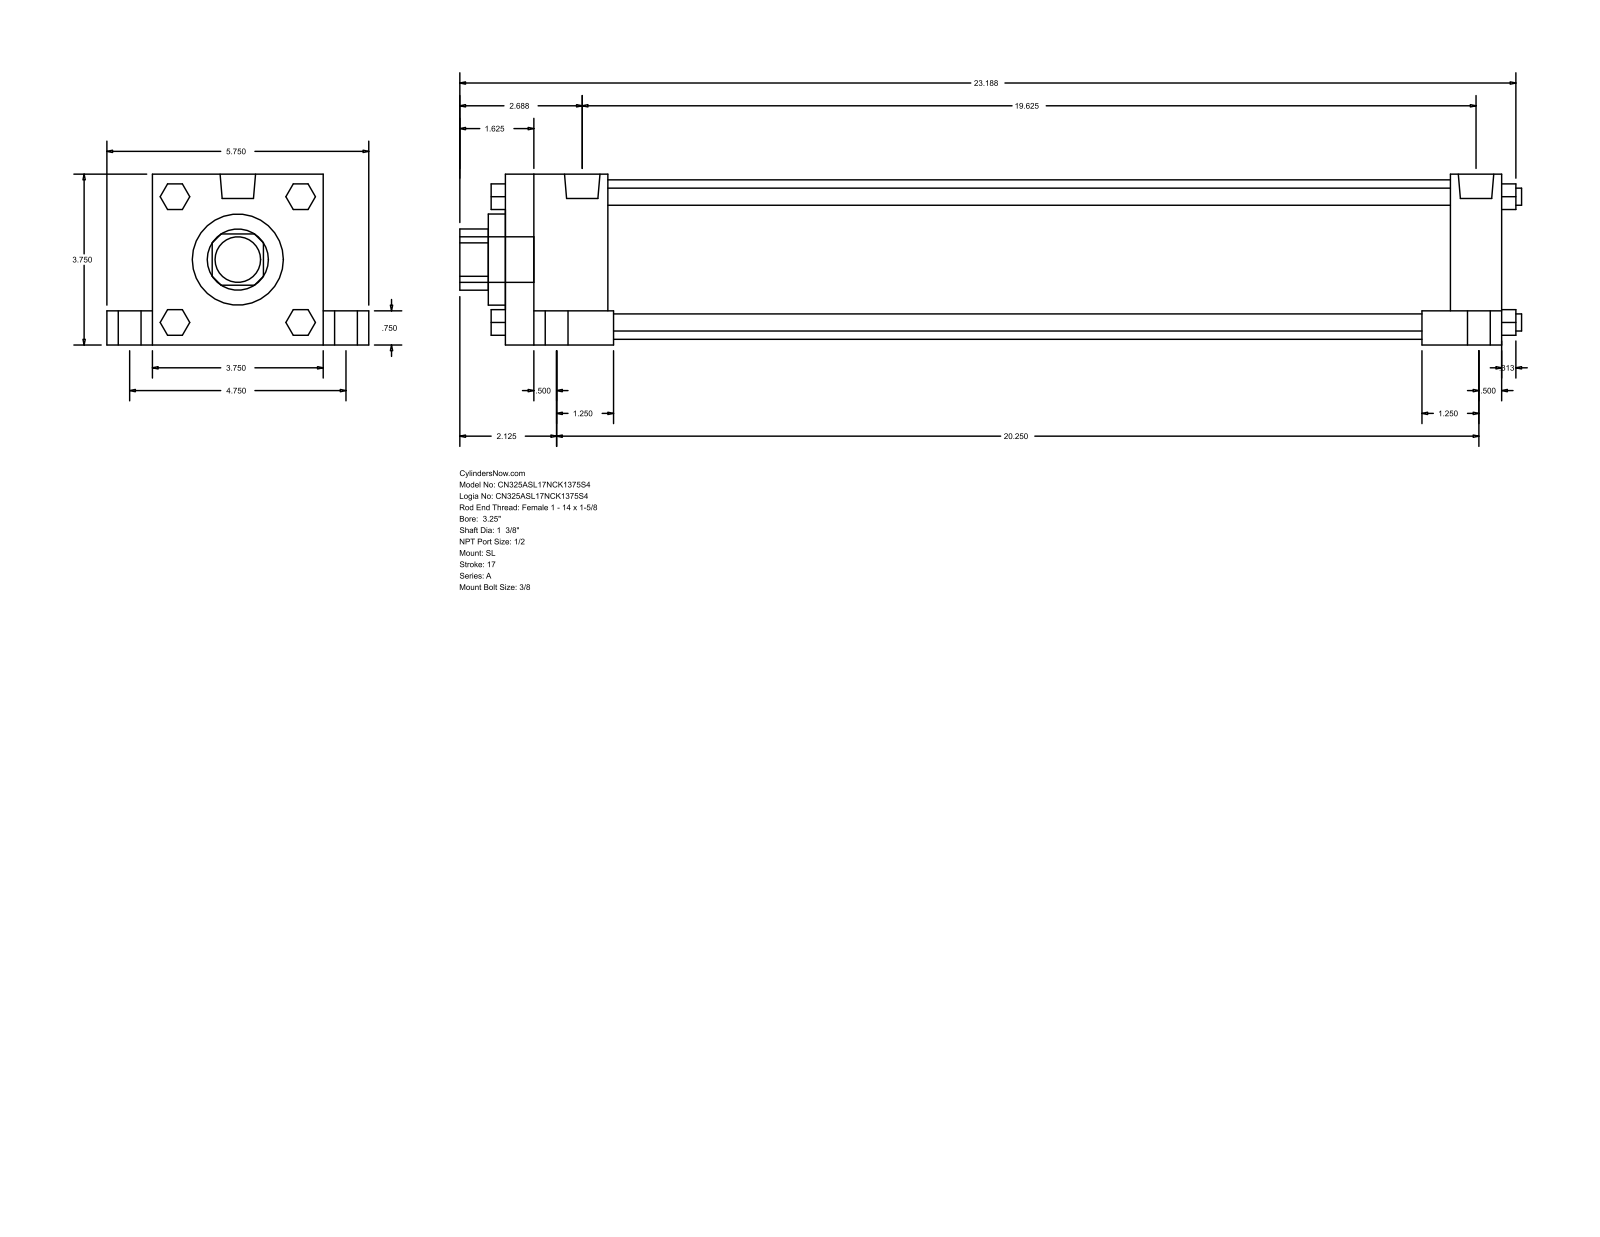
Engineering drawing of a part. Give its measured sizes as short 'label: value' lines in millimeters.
name: A_SL__0325_1.375
written by: GSSL Pune (CONFIG_CONTROL_DESIGN)
unit: mm
bodies: 0 solids, 150 faces (114 planar, 36 cylindrical, 0 other)
size: 592.14 × 146.05 × 95.25
holes: 1× ⌀34.92, 1× ⌀50.8, 1× ⌀88.9
bosses: 4× ⌀19.05, 4× ⌀12.7, 4× ⌀9.53, 4× ⌀8.73, 2× ⌀19.77, 1× ⌀25.4
rounds: 1× R17.06
face distances: 95.24, 555.62, 25.41, 120.65, 19.05, 76.19, 15.87, 28.57, 57.15, 527.05
